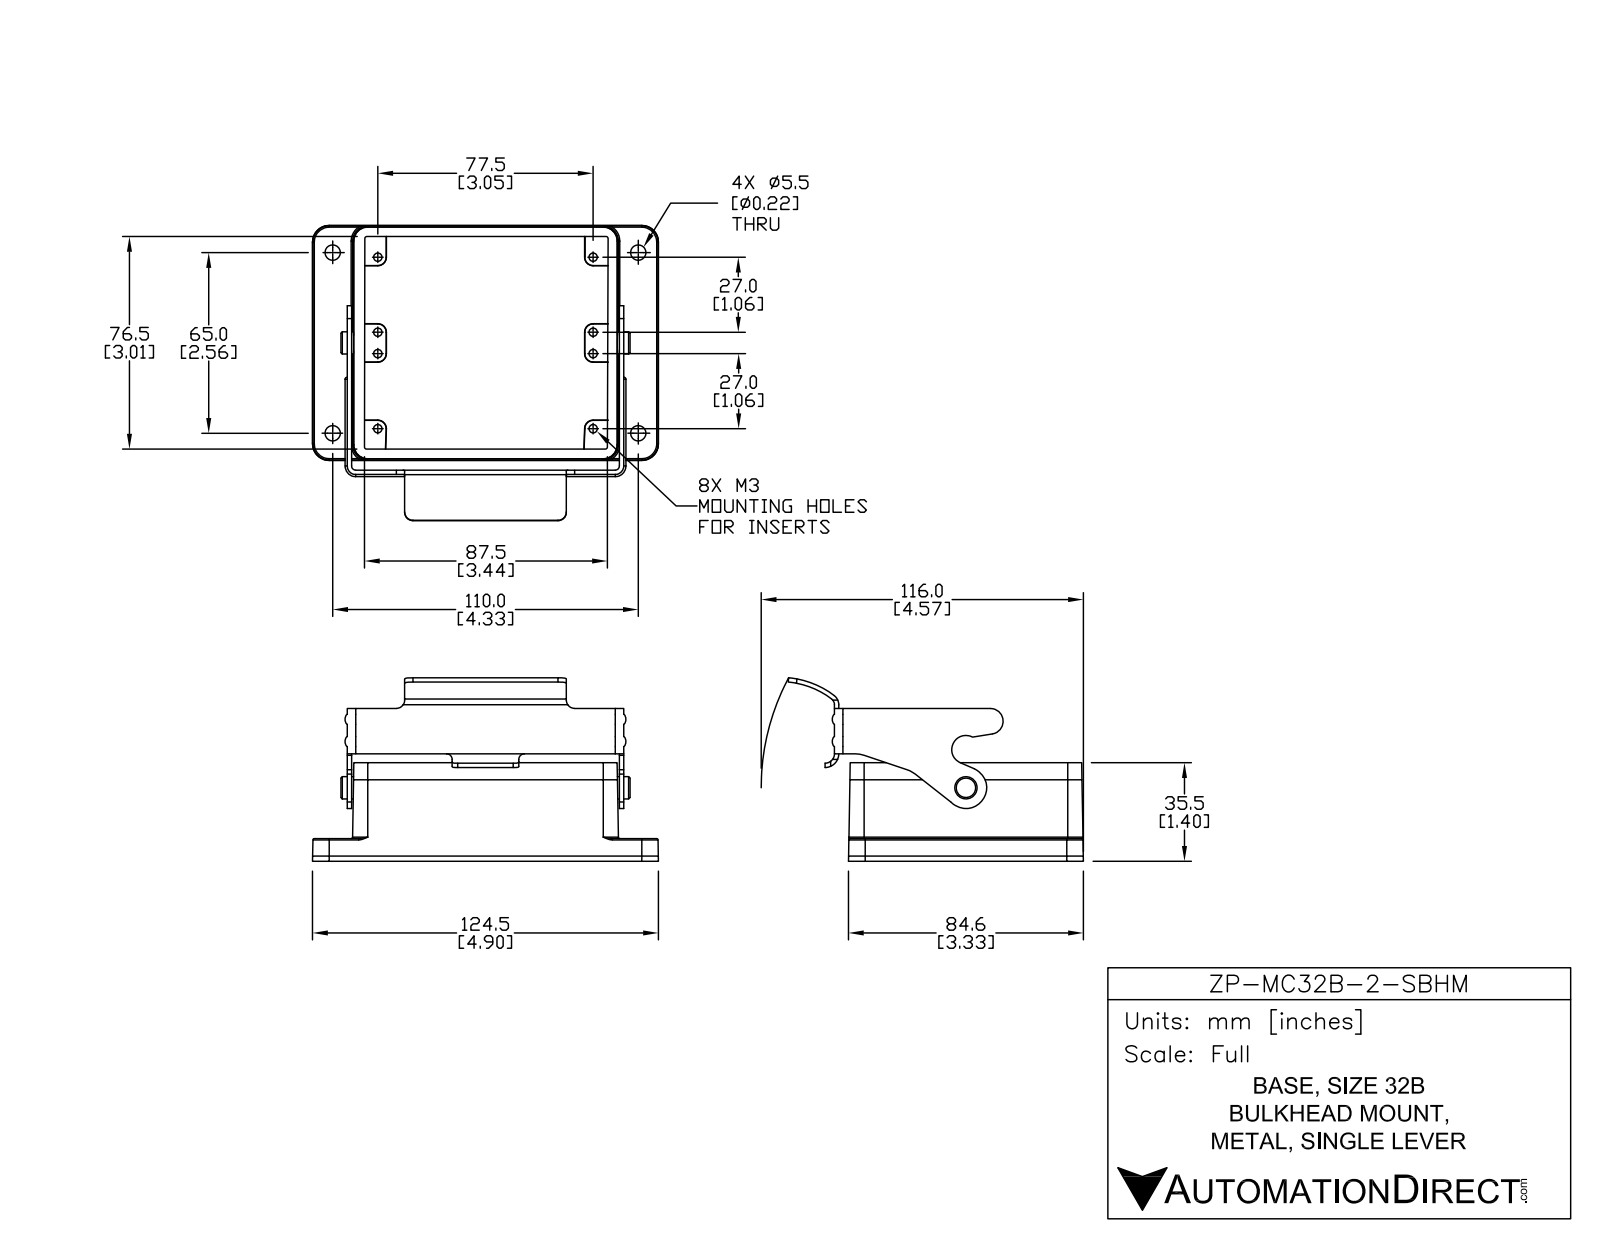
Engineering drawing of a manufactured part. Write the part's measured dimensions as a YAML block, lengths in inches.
part_name: "ZP-MC32B-2-SBHM"
step_written_by: "SolidWorks 2014 (AUTOMOTIVE_DESIGN)"
units: inches
bodies: {solids: 1, faces: 242, planar: 88, cylindrical: 100, other: 54}
overall_size: [4.902, 4.182, 2.593]
volume: 5.295
surface_area: 71.19
round_holes:
  - {diameter: 0.118, count: 8}
  - {diameter: 0.217, count: 4}
round_bosses_or_shafts:
  - {diameter: 0.315, count: 1}
partial_cylinders:
  - {radius: 0.02, count: 6}
  - {radius: 0.03, count: 4}
  - {radius: 0.079, count: 4}
  - {radius: 0.118, count: 4}
  - {radius: 0.236, count: 4}
  - {radius: 0.059, count: 2}
  - {radius: 0.12, count: 2}
  - {radius: 0.394, count: 2}
face_to_face_distances: [0.061, 2.946, 3.396, 0.323, 3.857, 3.275, 0.329, 1.39, 1.067, 0.2]
hole_center_spacings: [0.643, 1.063, 1.297, 1.366, 1.568, 2.575, 3.051, 3.231]
